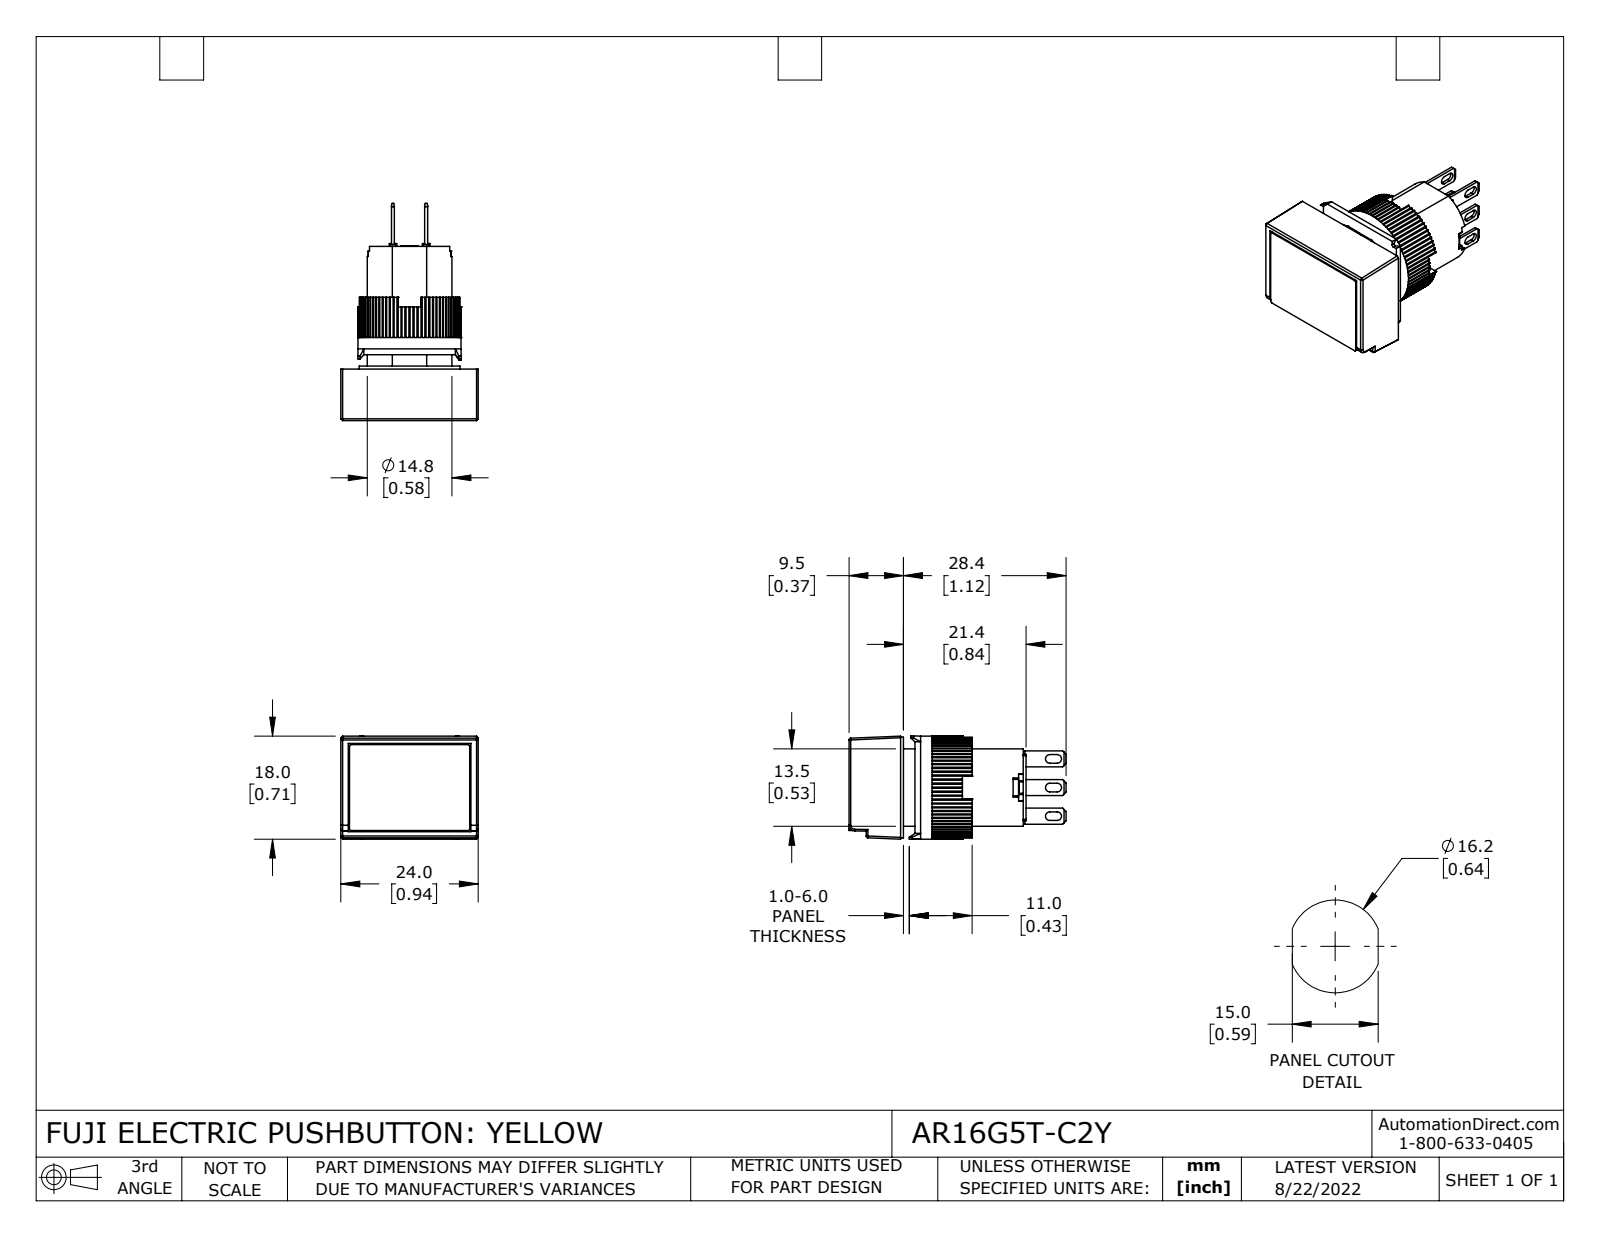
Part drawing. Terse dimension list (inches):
name: AR16G5T-C2Y
written by: SolidWorks 2021 (CONFIG_CONTROL_DESIGN)
unit: in
bodies: 12 solids, 811 faces (630 planar, 175 cylindrical, 6 other)
size: 1.492 × 0.945 × 0.709
volume: 0.447 in³; area: 9.321 in²
holes: 1× ⌀0.543, 1× ⌀0.583
bosses: 1× ⌀0.709, 1× ⌀0.693
rounds: 80× R0.01, 12× R0.008, 6× R0.012, 6× R0.03, 1× R0.039
face distances: 0.213, 0.354, 0.142, 0.492, 0.35, 0.138, 0.02, 0.843, 0.059, 0.453
